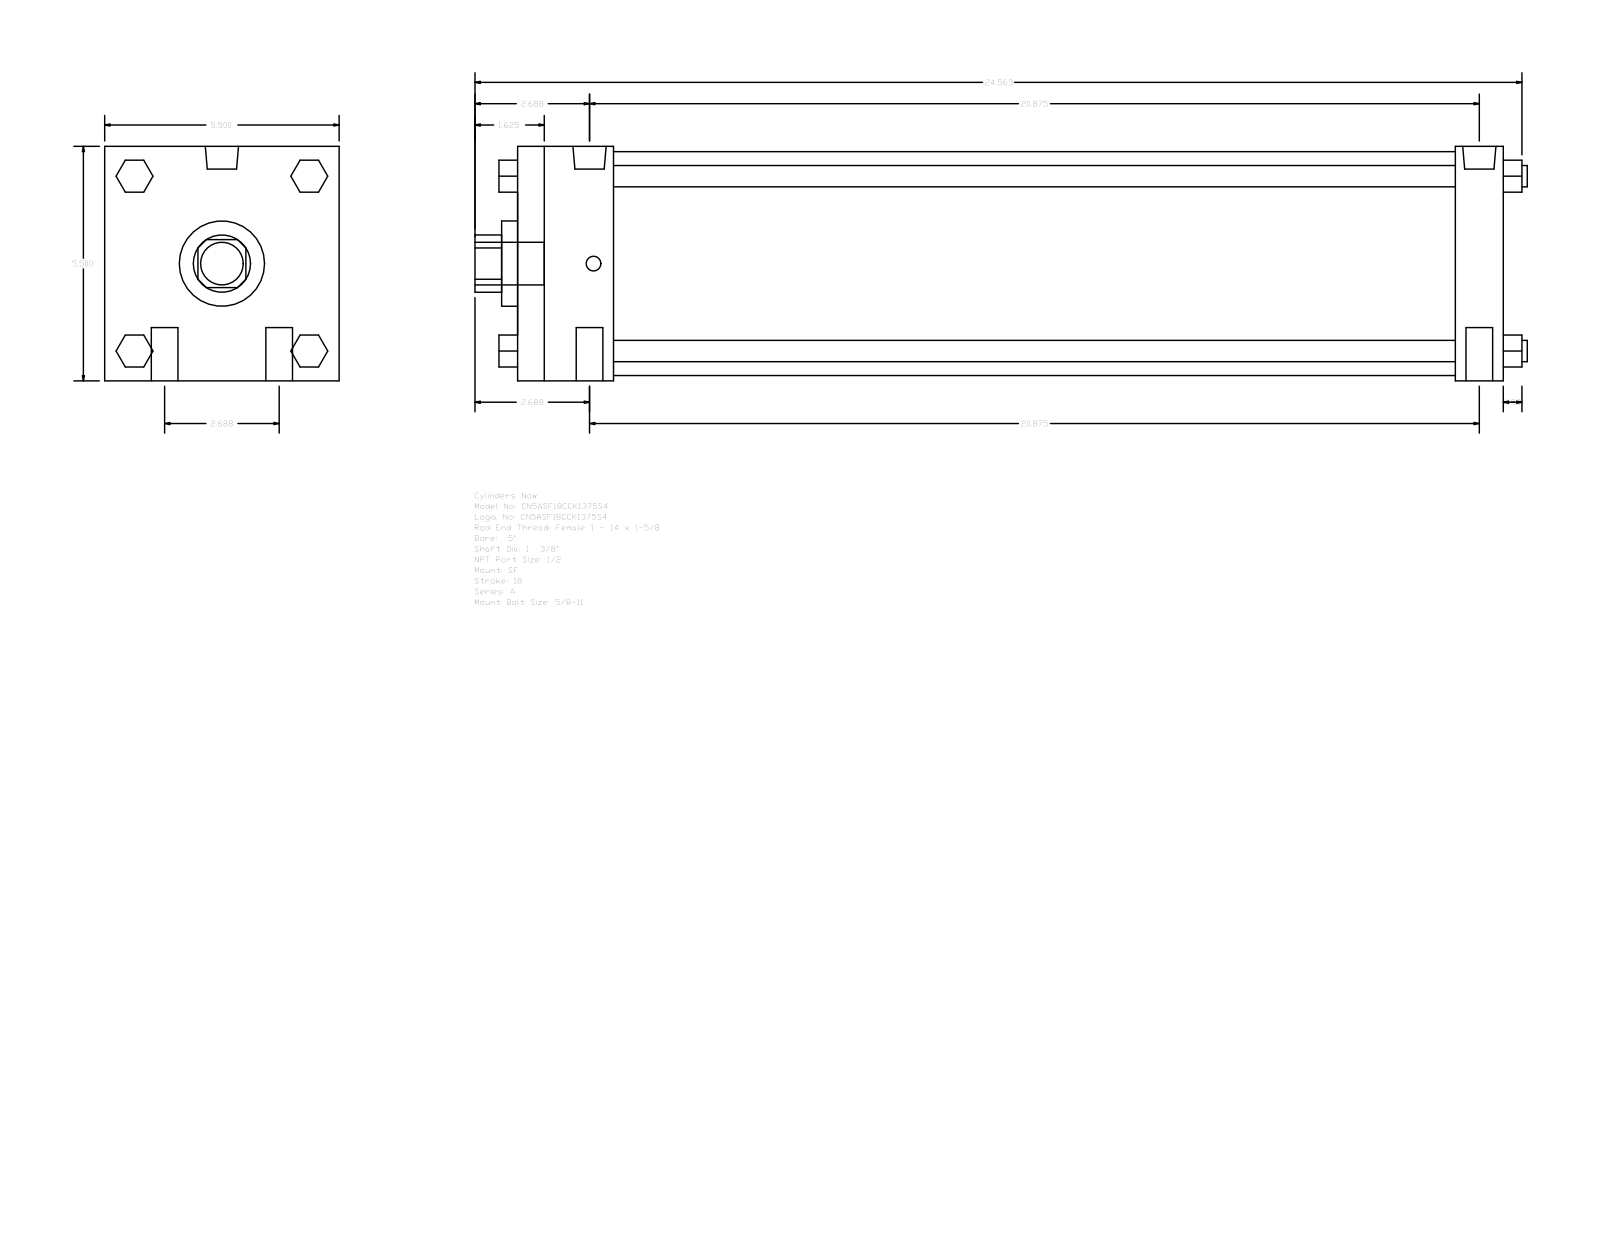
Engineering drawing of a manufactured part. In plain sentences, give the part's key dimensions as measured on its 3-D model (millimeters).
The part is named "A_SF__0500_1.375". Its 3-D file was written by "GSSL Pune (CONFIG_CONTROL_DESIGN)". It is 0 solids with 124 faces: 94 planar, 30 cylindrical and 0 other. Overall it measures 627.06 by 139.7 by 139.7 millimeters. Round holes: 1 of diameter 34.92, 1 of diameter 50.8, 1 of diameter 133.35. Round bosses or shafts: 4 of diameter 15.88, 4 of diameter 12.7, 2 of diameter 19.77, 2 of diameter 8.73, 1 of diameter 25.4. Partial cylindrical surfaces (rounded edges, fillets, slot ends): 1 of radius 17.06. The main face-to-face distances are 139.7, 587.37, 28.57, 57.15, 558.8, 501.65, 530.22, 19.05, 52.07, 90.18.
